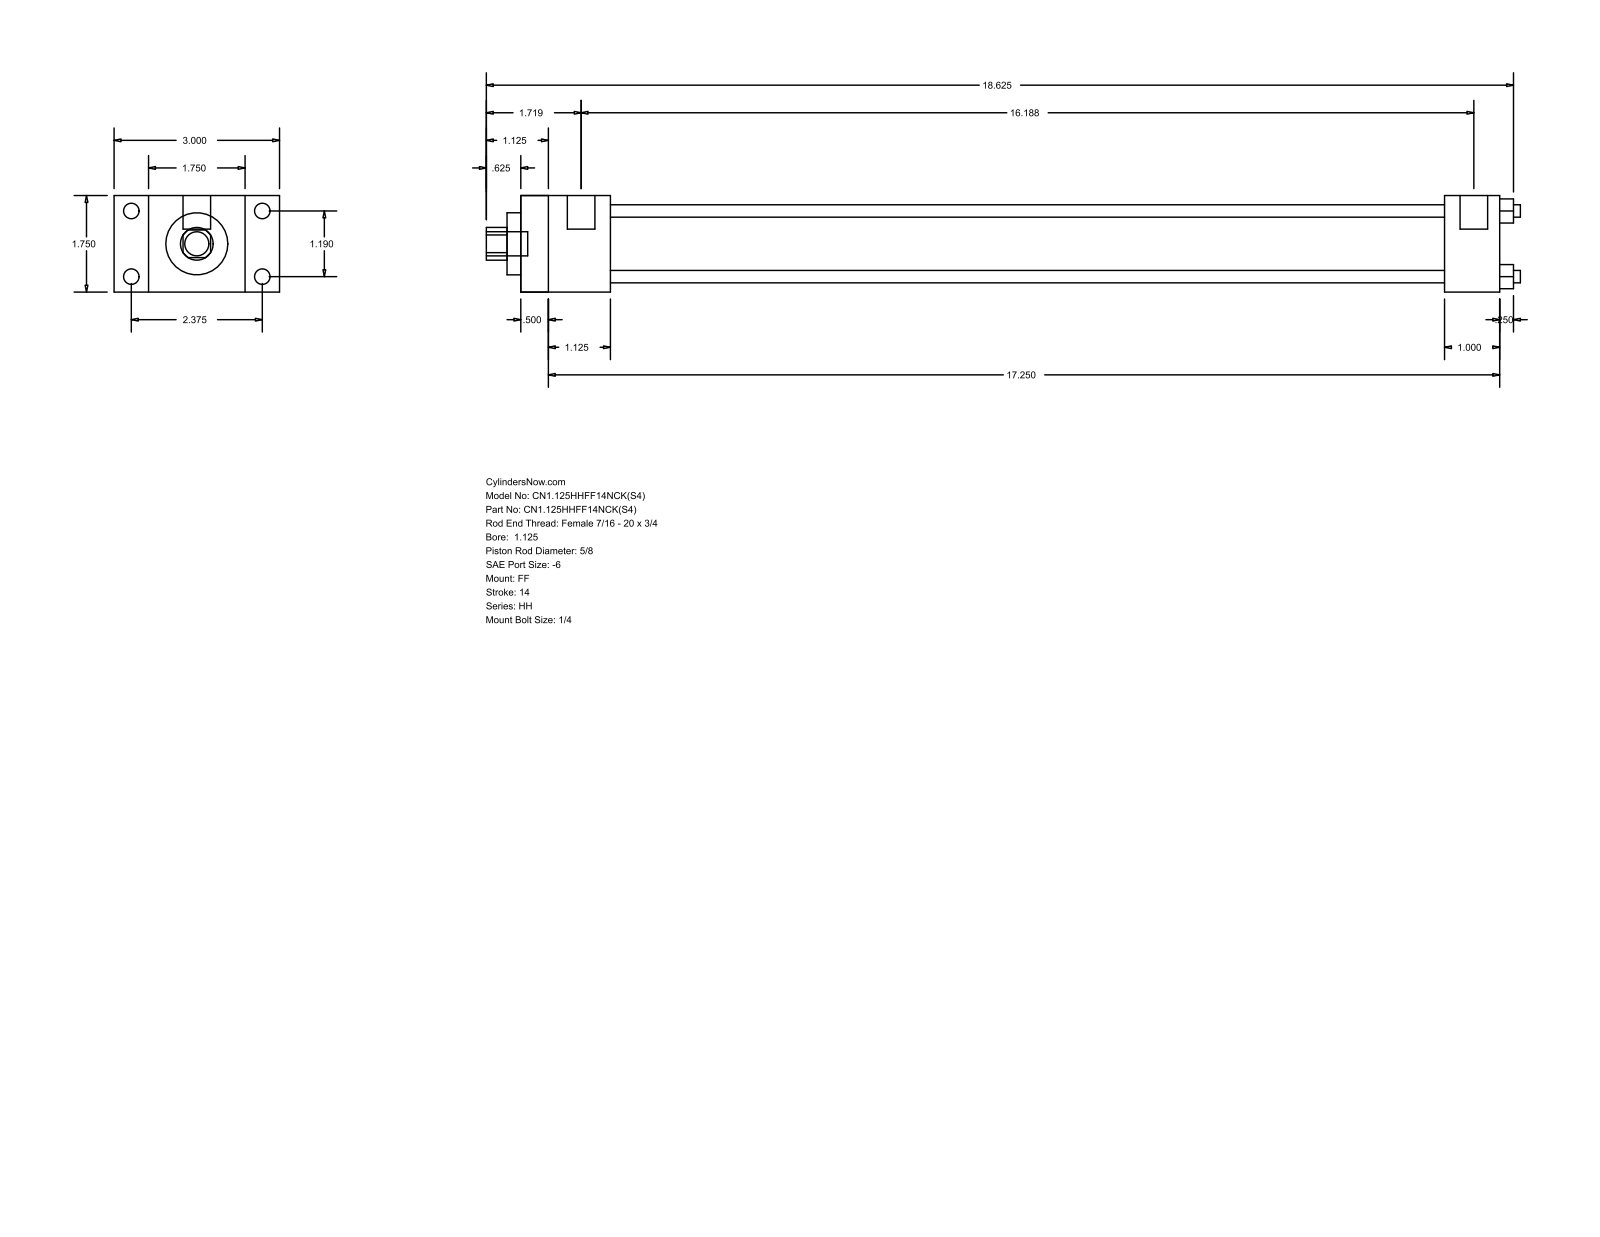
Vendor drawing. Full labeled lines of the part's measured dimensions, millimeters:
Part name (STEP PRODUCT): HH_FF__0112_0.625
STEP written by: GSSL Pune (CONFIG_CONTROL_DESIGN)
Units: millimetres
Bodies: 0 solids, 92 faces (64 planar, 28 cylindrical, 0 other)
Overall size (bounding box): 476.25 × 76.2 × 44.45
Round holes (diameter × count): ⌀5.71 ×4, ⌀15.88 ×1, ⌀28.57 ×1, ⌀34.92 ×1
Round bosses / shafts (diameter × count): ⌀7.14 ×4, ⌀5.56 ×4, ⌀12.7 ×2, ⌀11.11 ×1
Partial cylindrical surfaces — rounded edges, fillets, slot ends (radius × count): R7.54 ×1
Main face-to-face distances: 44.46, 450.85, 15.87, 12.69, 438.16, 60.33, 28.58, 41.27, 425.44, 412.75
Hole centre spacings: 21.37, 30.22, 42.74
